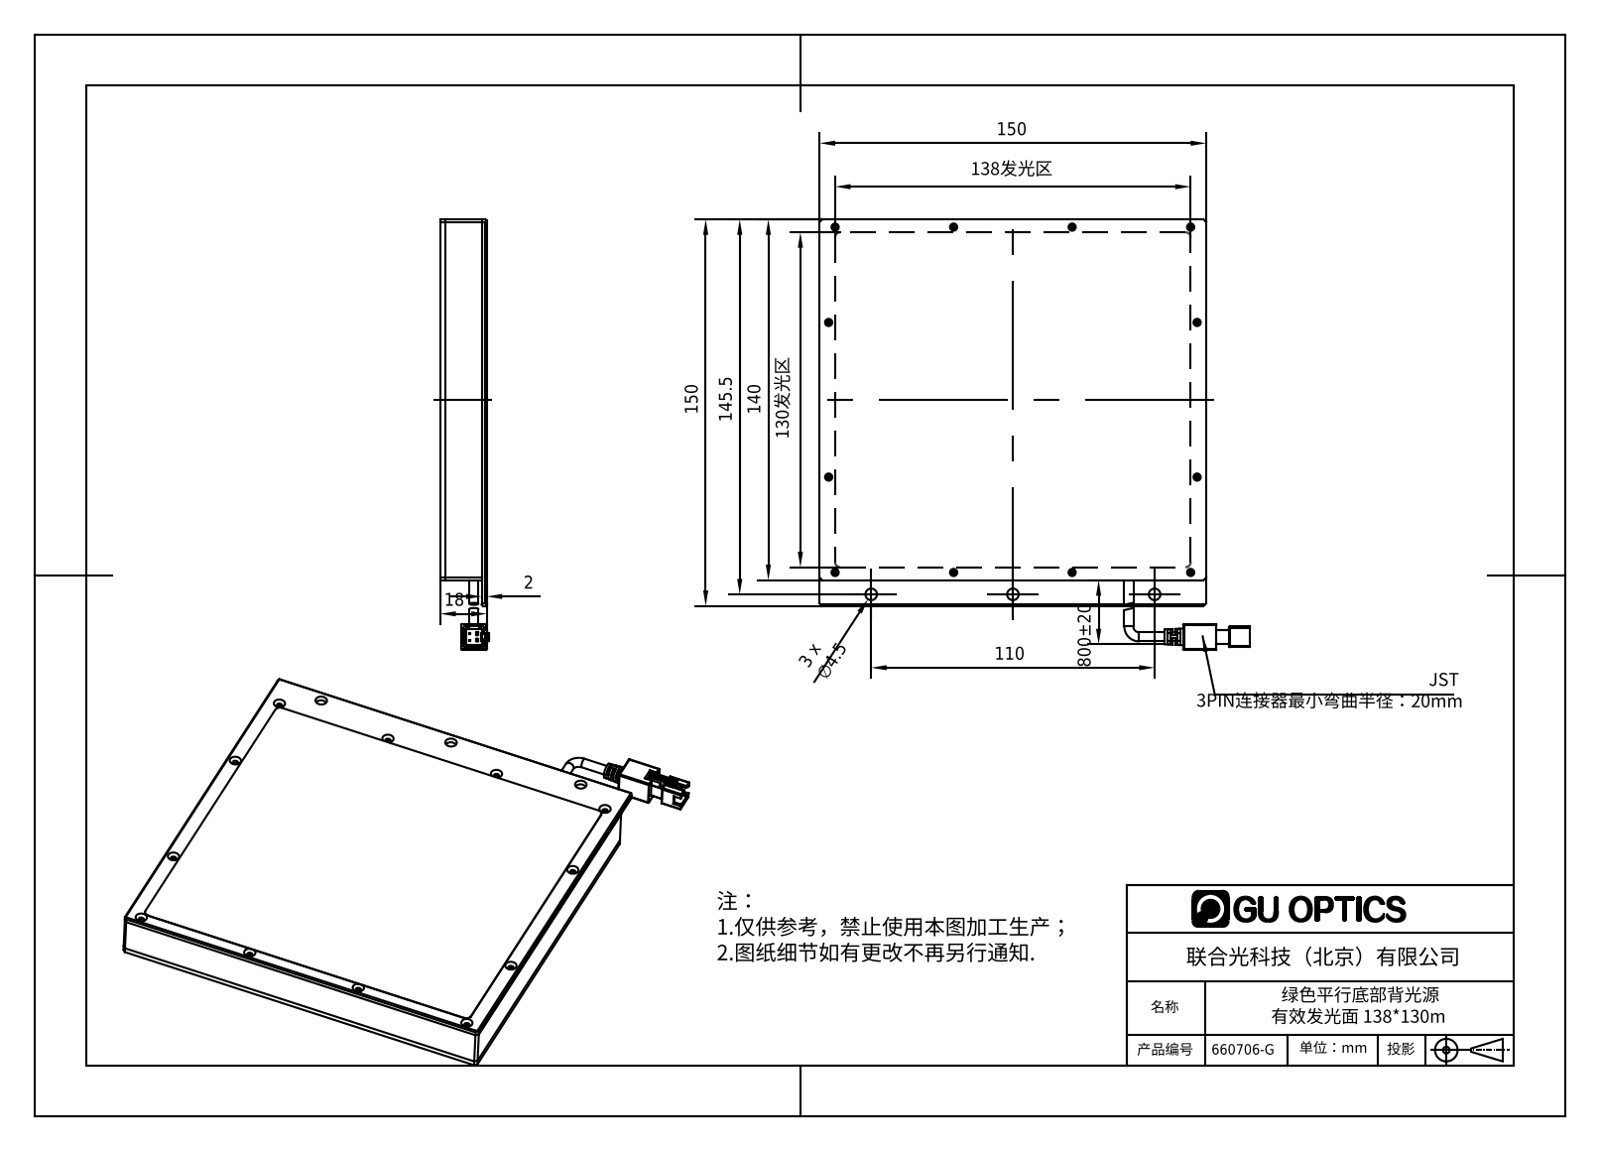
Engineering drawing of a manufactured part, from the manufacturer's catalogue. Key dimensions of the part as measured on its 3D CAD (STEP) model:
Part name (STEP PRODUCT): 660706-G
STEP written by: SolidWorks 2016 (AUTOMOTIVE_DESIGN)
Units: millimetres
Bodies: 22 solids, 3025 faces (2614 planar, 253 cylindrical, 158 other)
Overall size (bounding box): 167 × 167 × 18.7
Volume: 172 695 mm³ · Surface area: 157 551 mm²
Round holes (diameter × count): ⌀1.1 ×12, ⌀1.4 ×12, ⌀1.5 ×12, ⌀1.6 ×12, ⌀2 ×12, ⌀2.2 ×12, ⌀2.8 ×12, ⌀4.5 ×3
Round bosses / shafts (diameter × count): ⌀3.5 ×2
Partial cylindrical surfaces — rounded edges, fillets, slot ends (radius × count): R0.1 ×15, R0.2 ×13, R0.4 ×12, R1 ×4, R2 ×4, R1.5 ×2, R0.3 ×1, R0.68 ×1
Main face-to-face distances: 2, 14, 16, 2.1, 16.1, 18.1, 12, 4.1, 5, 1
Hole centre spacings: 46, 141.68, 37.08, 61, 92, 97.03, 101.49, 108.45
